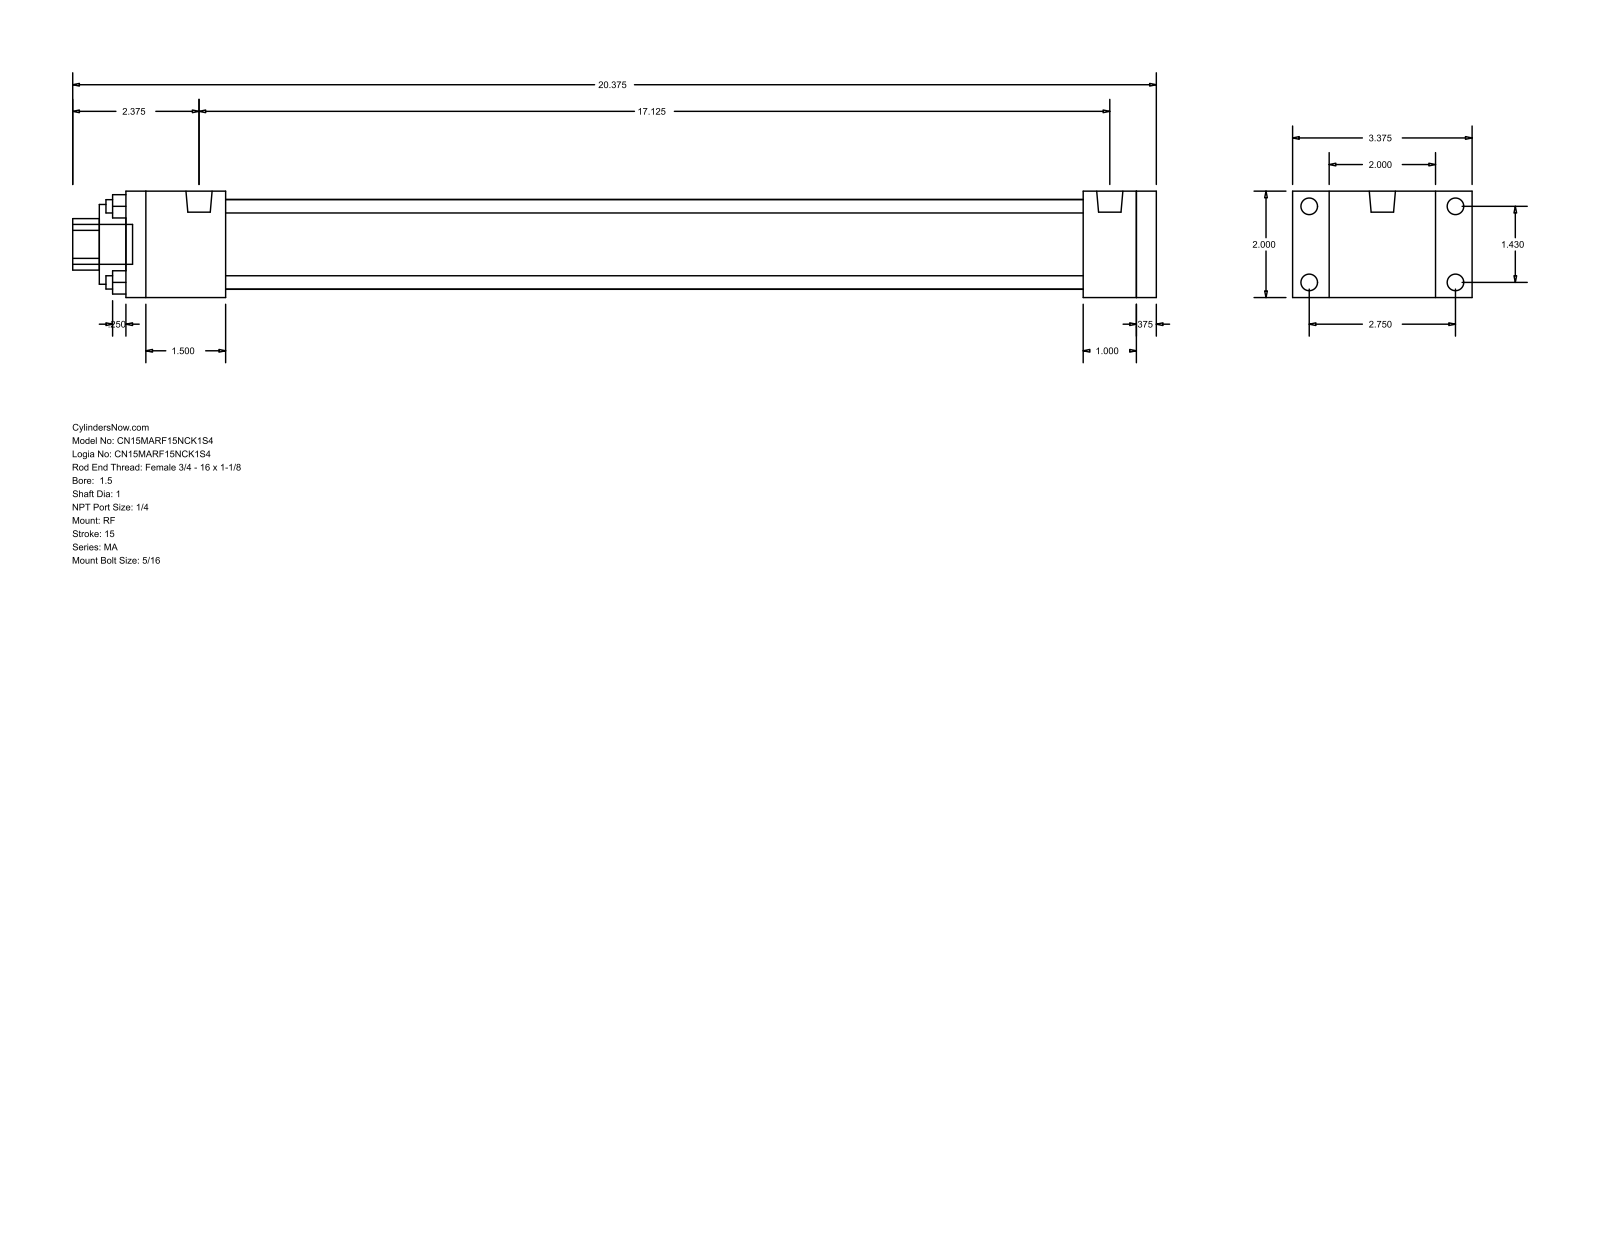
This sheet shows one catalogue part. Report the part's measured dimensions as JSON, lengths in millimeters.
{"part_name": "MA_RF__0150_1", "step_written_by": "GSSL Pune (CONFIG_CONTROL_DESIGN)", "units": "millimeters", "bodies": {"solids": 0, "faces": 92, "planar": 64, "cylindrical": 28, "other": 0}, "overall_size": [517.52, 85.72, 50.8], "round_holes": [[6.35, 4], [25.4, 1], [38.1, 1], [42.93, 1]], "round_bosses_or_shafts": [[7.94, 8], [12.49, 2], [19.05, 1]], "partial_cylinders_radius": [[12.29, 1]], "face_to_face_distances": [50.8, 9.52, 492.12, 482.6, 25.4, 457.2, 34.92, 47.63, 409.57, 434.97], "hole_center_spacings": [25.68, 36.32, 51.36]}
